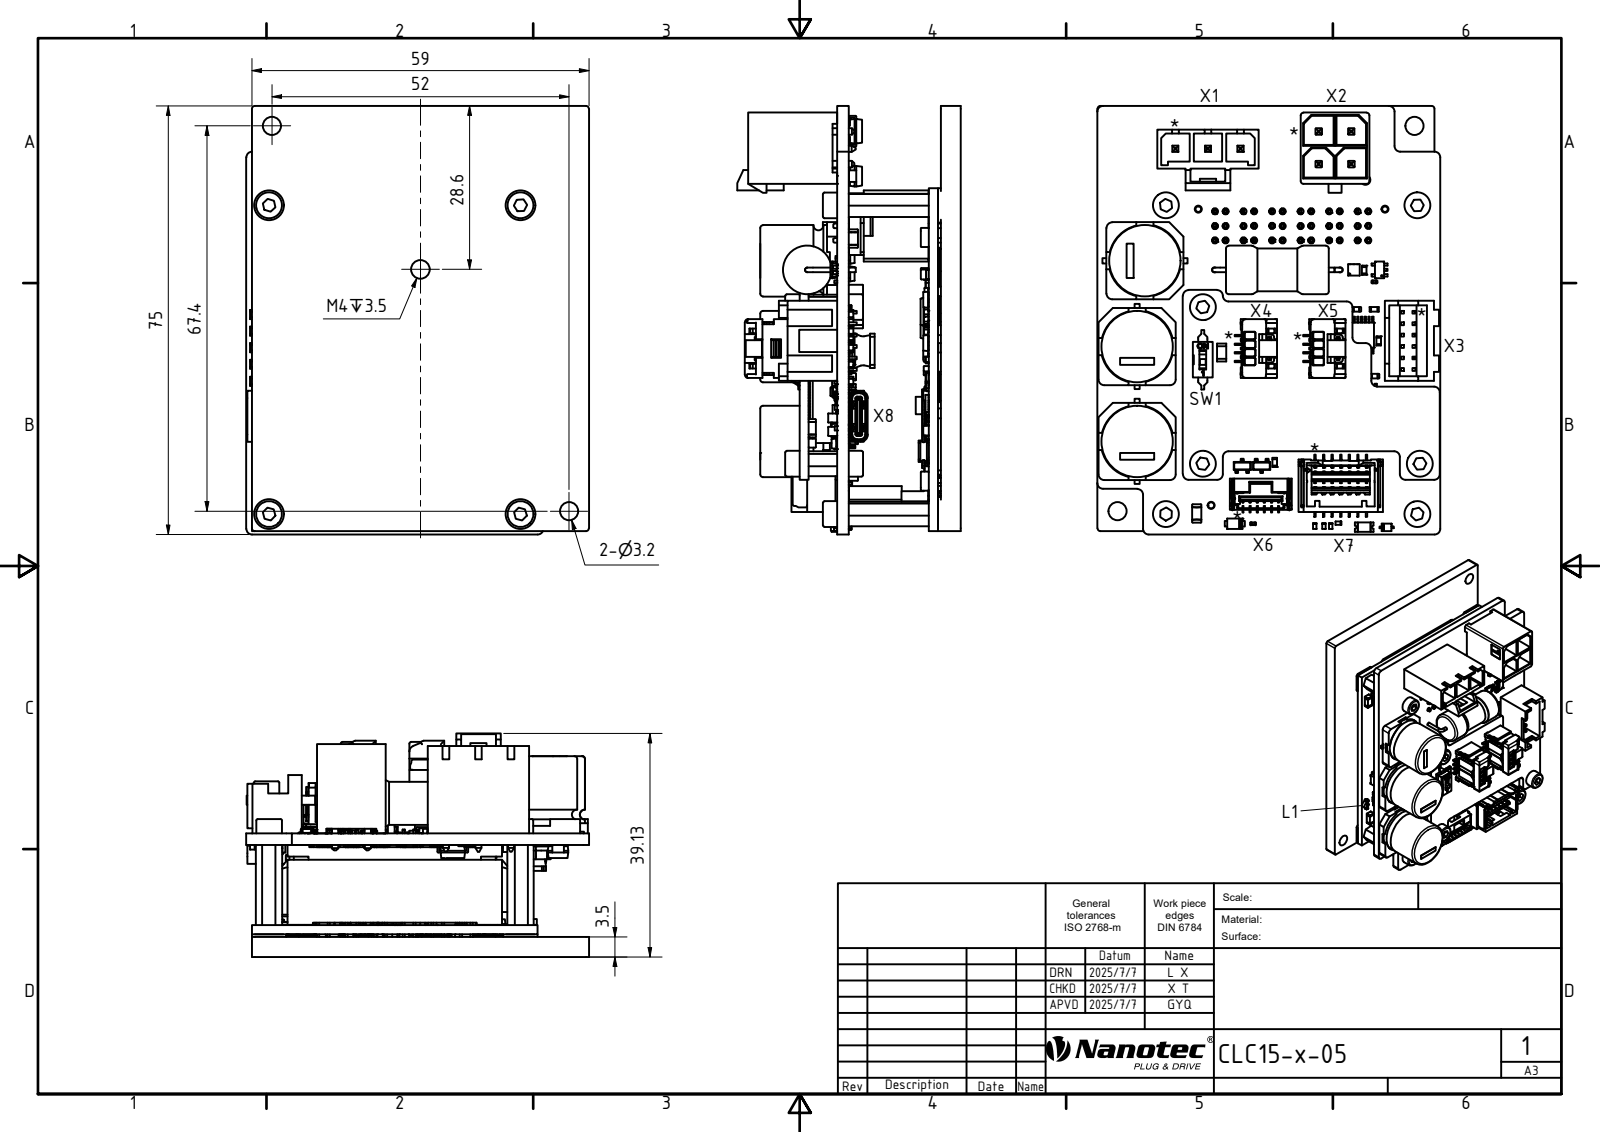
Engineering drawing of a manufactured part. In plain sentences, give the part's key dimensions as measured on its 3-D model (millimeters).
The part is named "CLC15-x-05". Its 3-D file was written by "Autodesk Inventor 2024 (AUTOMOTIVE_DESIGN)". It is 0 solids with 30231 faces: 19128 planar, 7720 cylindrical and 3383 other. Overall it measures 75 by 60 by 39.13 millimeters. Round holes: 43 of diameter 1.05, 12 of diameter 0.7, 8 of diameter 1.7, 7 of diameter 2.01, 7 of diameter 2.7, 6 of diameter 1.6, 5 of diameter 1.2, 4 of diameter 0.25, 4 of diameter 0.3, 4 of diameter 0.6, 4 of diameter 5.2, 3 of diameter 0.43. Round bosses or shafts: 7 of diameter 4.5, 7 of diameter 2.5, 7 of diameter 1.4, 6 of diameter 0.4, 5 of diameter 1, 4 of diameter 0.8, 3 of diameter 12.5, 2 of diameter 3. Partial cylindrical surfaces (rounded edges, fillets, slot ends): 1022 of radius 0.1, 164 of radius 0.2, 158 of radius 0.12, 84 of radius 1, 62 of radius 0.15, 37 of radius 0.5, 32 of radius 0.3, 26 of radius 0.13. The main face-to-face distances are 2.03, 19.61, 21.64, 0.5, 4, 17.64, 15.61, 16.11, 3.5, 18.14. The hole center spacings are 5.61, 5, 10.32, 10, 1.88, 7.13, 3.12, 6.88.
